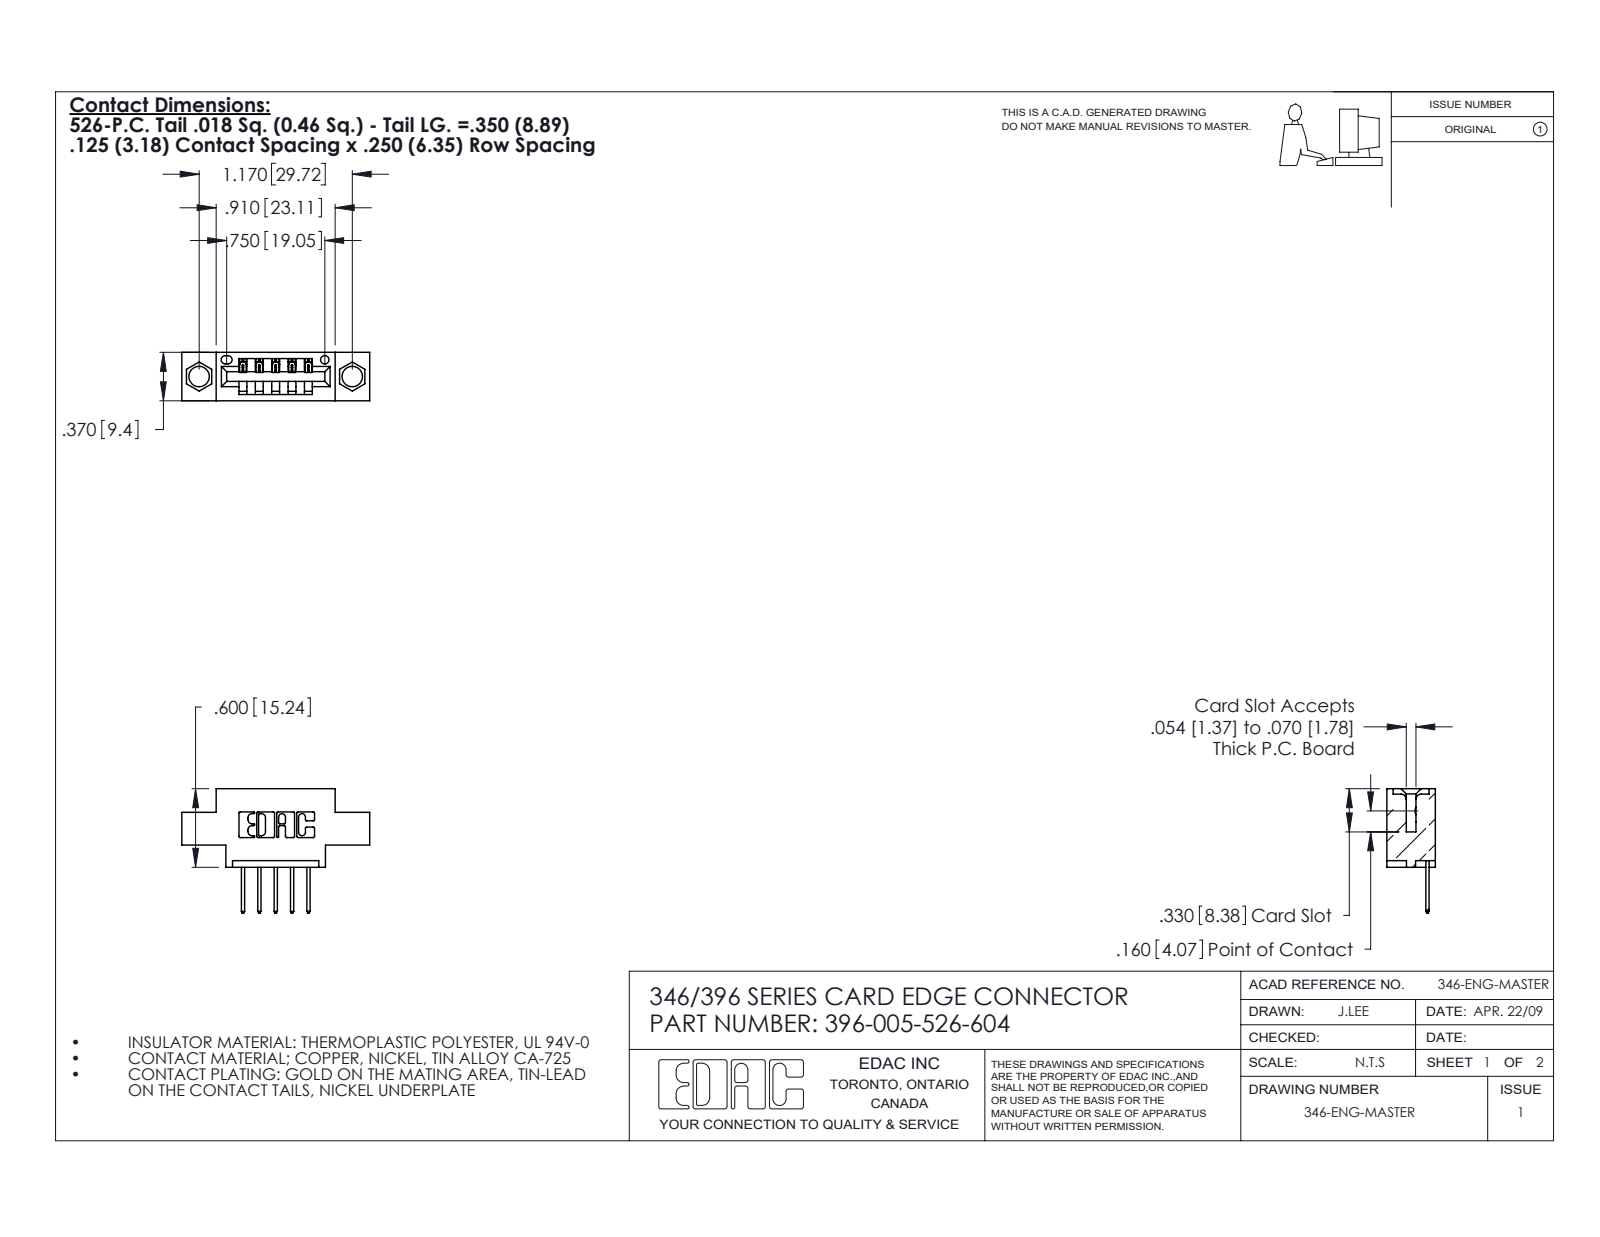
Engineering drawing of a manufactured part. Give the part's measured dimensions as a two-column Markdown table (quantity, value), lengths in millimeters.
| quantity | value |
| --- | --- |
| part name | 346 Part_0.170 Offset - 0.156 Dia-TH; 345-292-001_345-293-126; 396-005-526-604 |
| STEP written by | SolidWorks 2020 (CONFIG_CONTROL_DESIGN) |
| units | millimeters |
| bodies | 6 solids, 430 faces (294 planar, 136 cylindrical, 0 other) |
| overall size | 36.4 × 24.1 × 9.4 |
| volume | 2 970 mm³ |
| surface area | 3 305 mm² |
| round holes (diameter × count) | 4 × 2, 1.6 × 1 |
| partial cylindrical surfaces (radius × count) | 0.3 × 22, 0.2 × 10, 0.3 × 10, 0.2 × 6, 0.8 × 6, 0.7 × 3, 0.8 × 2, 1 × 2 |
| main face-to-face distances | 6.4, 9.4, 1.2, 8.2, 5.6, 3.8, 2.5, 4.4, 14, 1.8 |
| hole center spacings | 6.2, 24.6, 29.7 |
